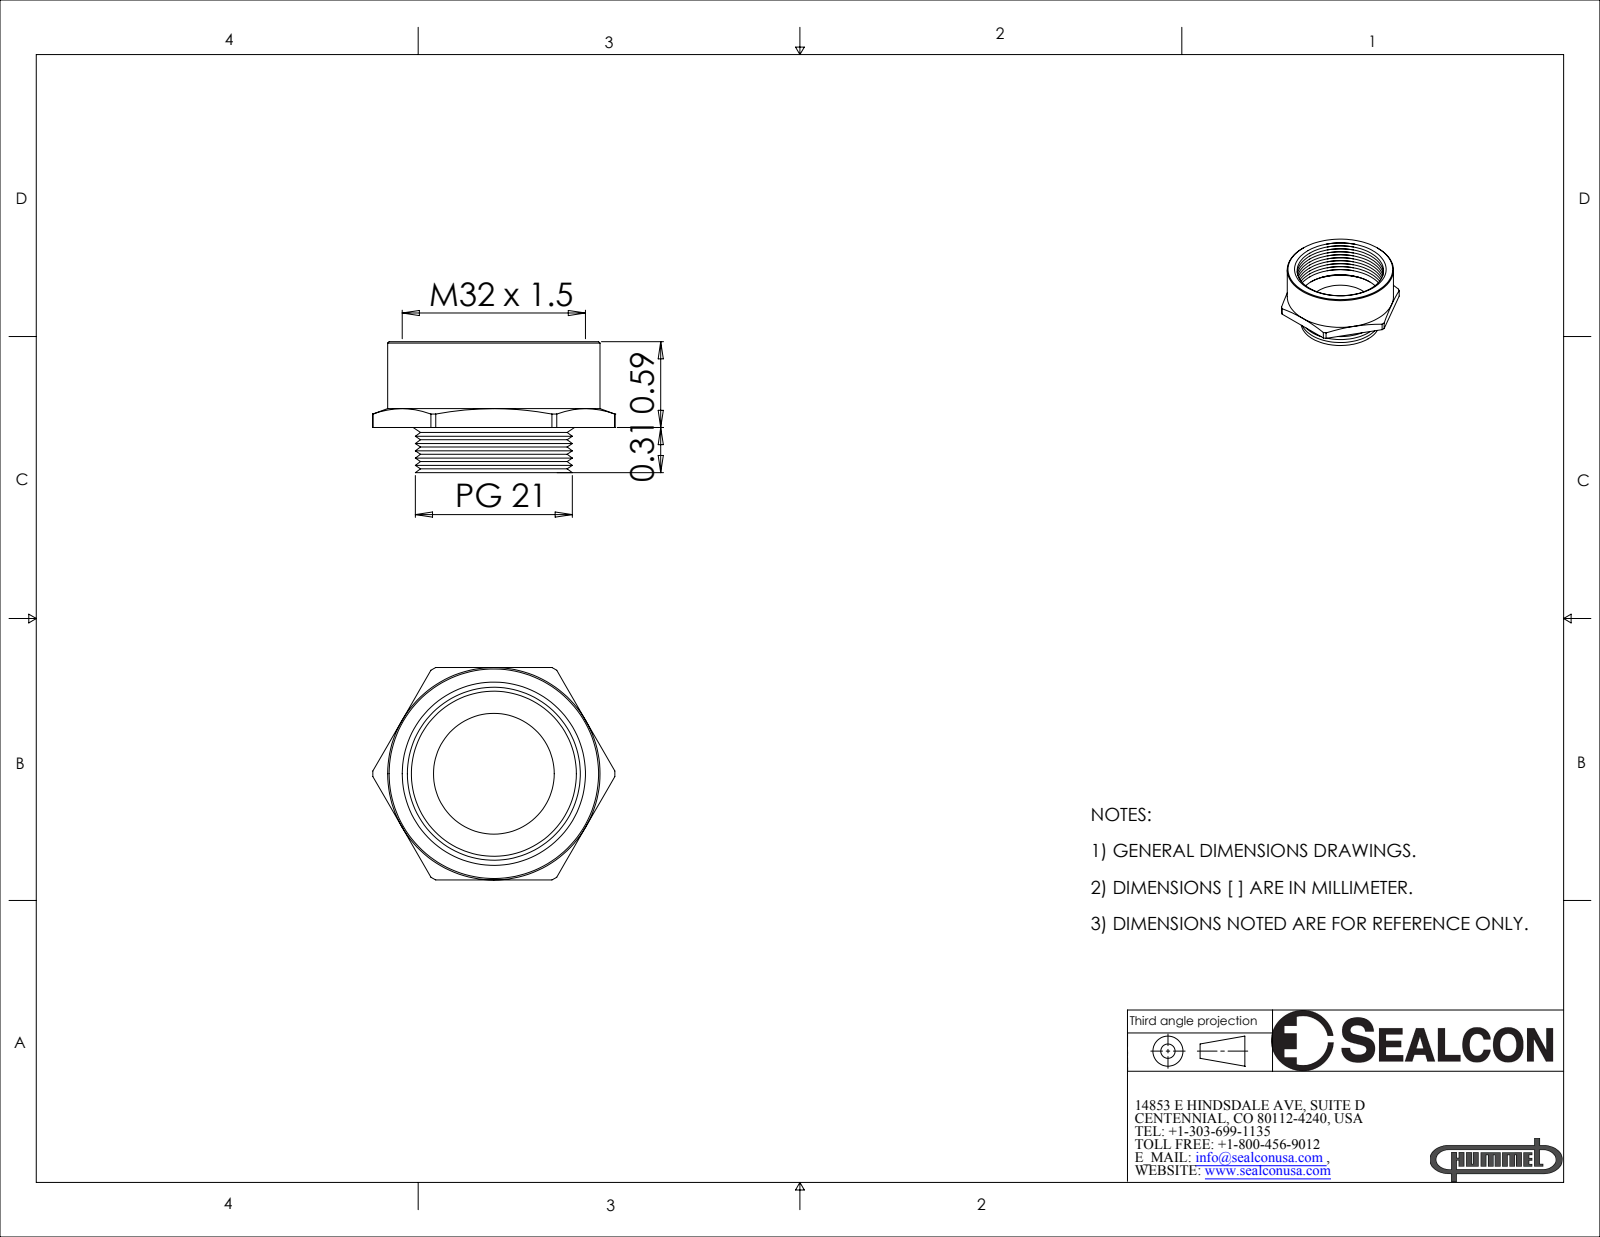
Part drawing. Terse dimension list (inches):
name: AP-2132-BK
written by: SolidWorks 2008 (CONFIG_CONTROL_DESIGN)
unit: in
bodies: 1 solid, 99 faces (11 planar, 13 cylindrical, 75 other)
size: 1.664 × 1.46 × 0.9
volume: 0.424 in³; area: 11.87 in²
holes: 1× ⌀0.83, 1× ⌀1.304
bosses: 1× ⌀1.46
rounds: 1× R0.832
face distances: 0.03, 0.59, 0.561, 0.31, 0.339, 0.9, 0.398, 0.089, 0.059, 0.502
